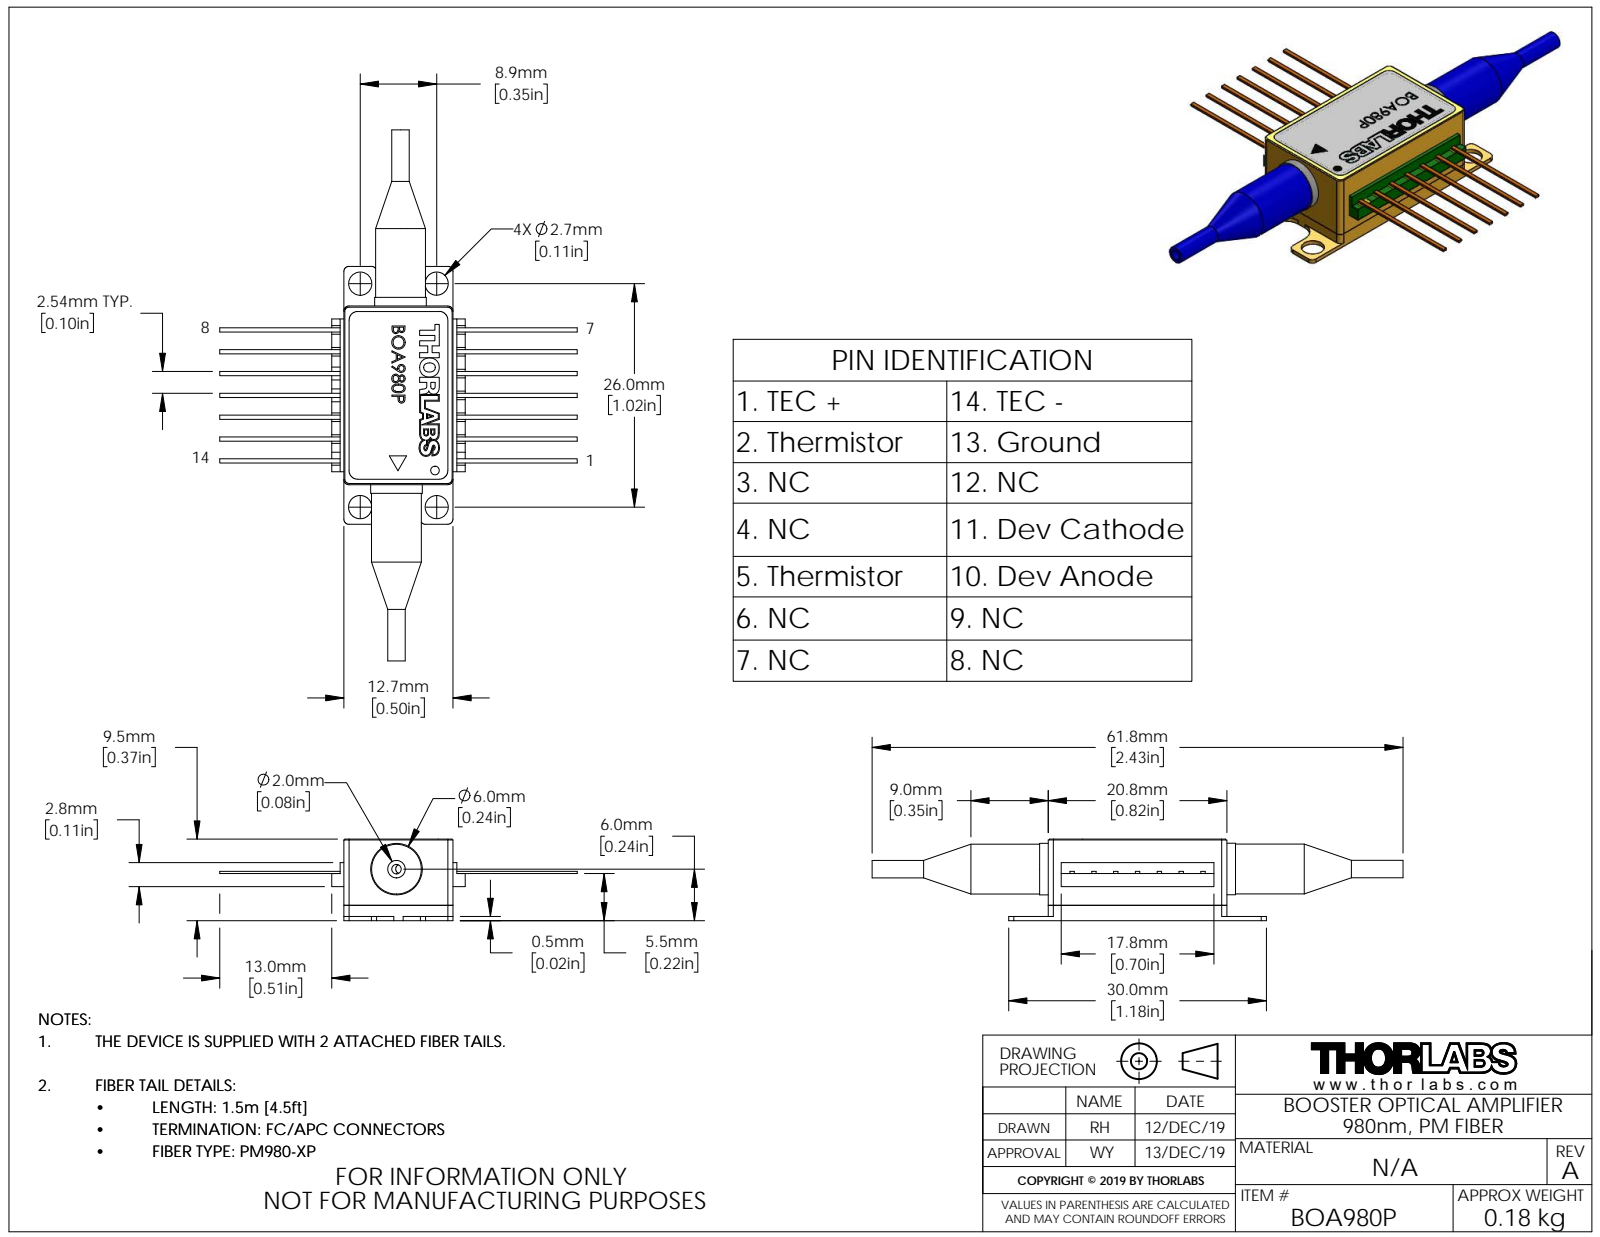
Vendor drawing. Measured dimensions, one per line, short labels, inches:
name: QTN039464-E0W
written by: SolidWorks 2018 (AUTOMOTIVE_DESIGN)
unit: in
bodies: 0 solids, 389 faces (264 planar, 50 cylindrical, 75 other)
size: 2.433 × 1.638 × 0.374
holes: 4× ⌀0.106, 2× ⌀0.043, 1× ⌀0.039
bosses: 2× ⌀0.236, 2× ⌀0.228, 2× ⌀0.08
rounds: 12× R0.024, 4× R0.02, 4× R0.079
face distances: 0.374, 0.5, 0.071, 0.303, 0.156, 0.085, 0.218, 0.146, 0.217, 0.06
hole spacings: 0.35, 1.024, 1.082, 0.019, 0.168, 0.381, 0.856, 0.922
